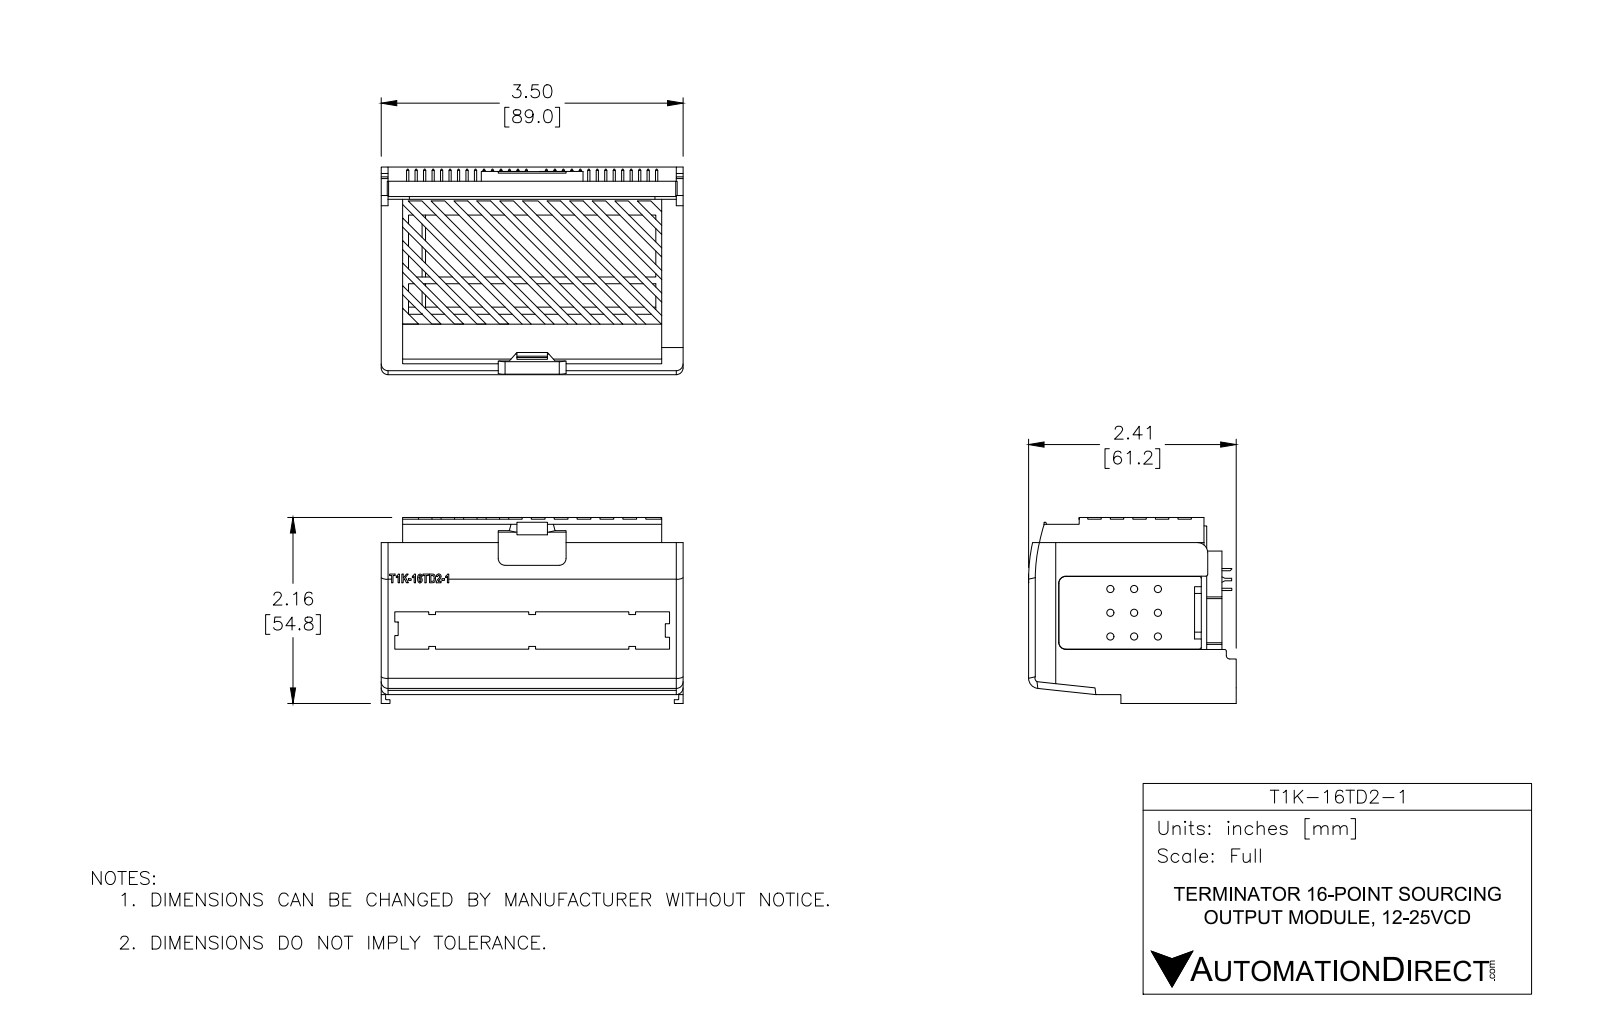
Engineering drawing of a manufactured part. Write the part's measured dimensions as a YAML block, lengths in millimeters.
part_name: "T1K-16TD2-1"
step_written_by: "SolidWorks 2013 (AUTOMOTIVE_DESIGN)"
units: millimeters
bodies: {solids: 1, faces: 656, planar: 454, cylindrical: 181, other: 21}
overall_size: [88.7, 65.1, 61.36]
volume: 45450
surface_area: 54523
round_holes:
  - {diameter: 3, count: 16}
round_bosses_or_shafts:
  - {diameter: 0.7, count: 56}
partial_cylinders:
  - {radius: 3.5, count: 18}
  - {radius: 1, count: 5}
  - {radius: 0.25, count: 3}
  - {radius: 0.55, count: 3}
  - {radius: 1.5, count: 2}
  - {radius: 8, count: 1}
  - {radius: 10, count: 1}
  - {radius: 18, count: 1}
face_to_face_distances: [2, 86.7, 55.35, 0.5, 59.8, 88.7, 1.5, 55.26, 53.35, 84.7]
hole_center_spacings: [5.15, 10.3, 15.45, 20.6, 25.75, 30.9, 36.05, 41.2]
